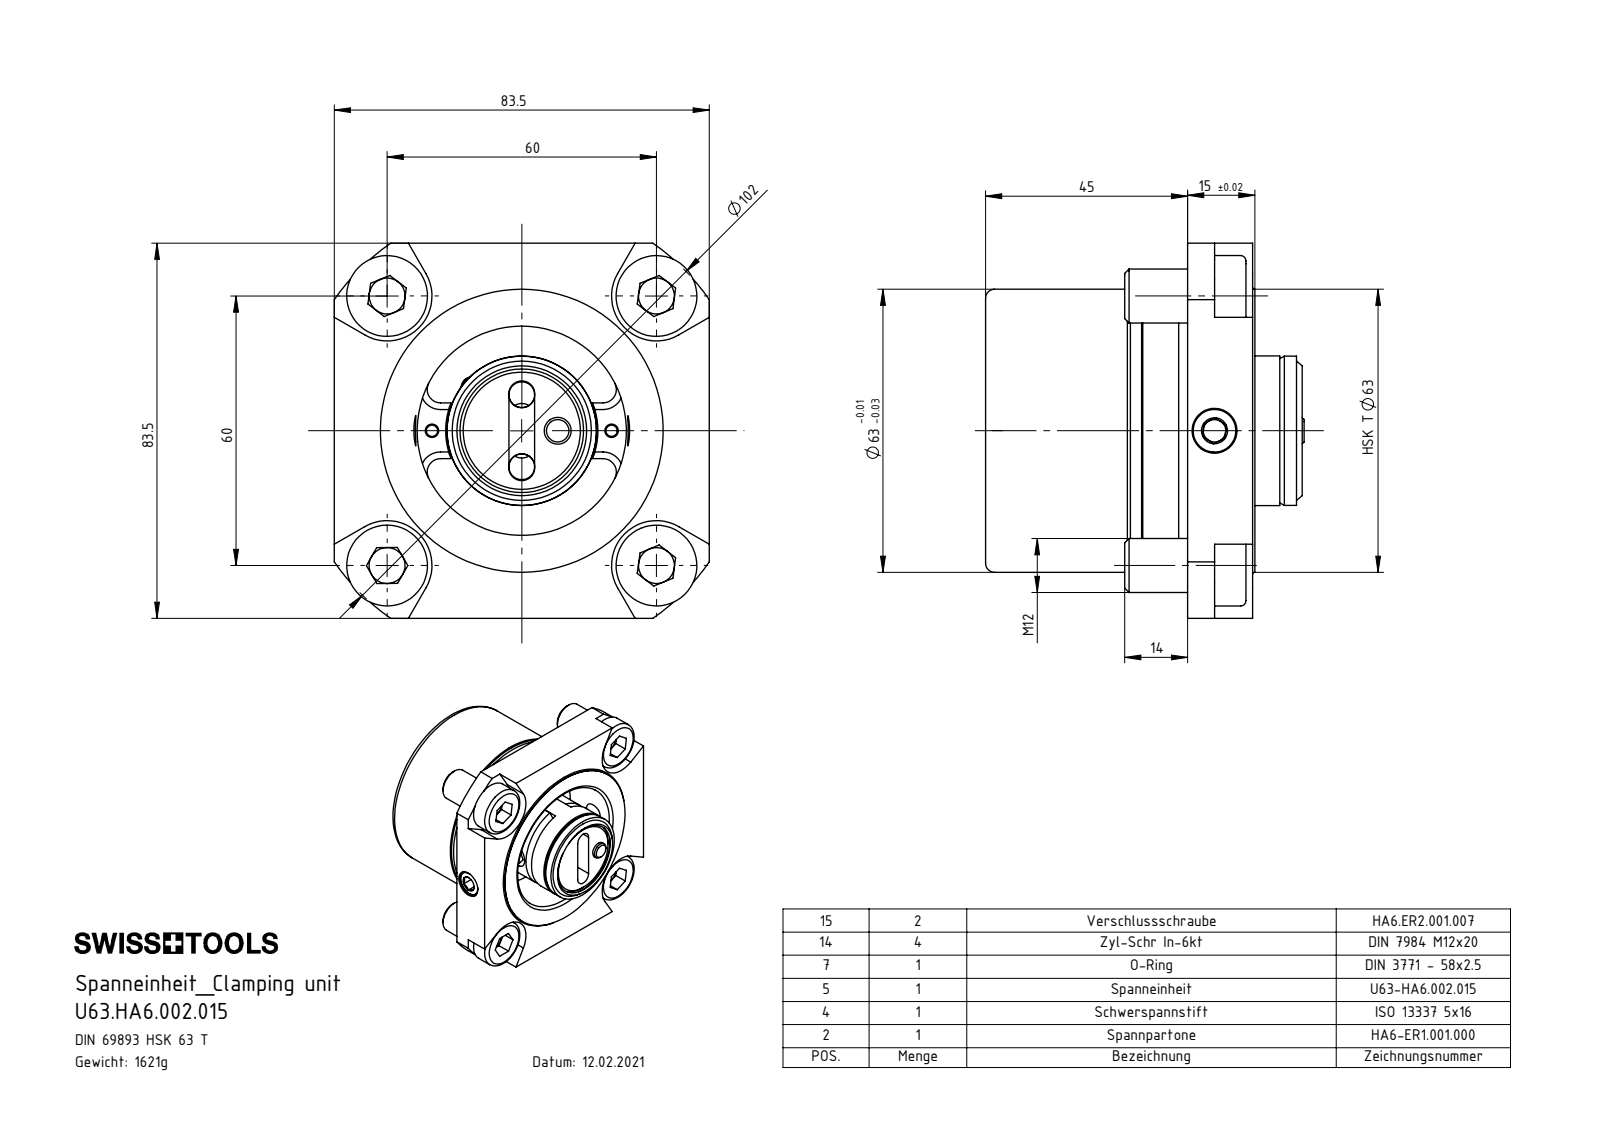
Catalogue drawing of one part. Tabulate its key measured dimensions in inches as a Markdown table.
| quantity | value |
| --- | --- |
| part name | DIN 3771 - 58x2.5; HA6-ER2.001.007; DIN 3771 - 17x2; Backe6 (+8 more) |
| STEP written by | SolidWorks 2022 (AUTOMOTIVE_DESIGN) |
| units | inches |
| bodies | 16 solids, 494 faces (196 planar, 151 cylindrical, 147 other) |
| overall size | 3.287 × 3.287 × 2.793 |
| volume | 12.67 in³ |
| surface area | 100.5 in² |
| round holes (diameter × count) | 0.512 × 4, 0.098 × 2, 0.226 × 2, 0.228 × 2, 0.394 × 2, 0.157 × 1, 0.197 × 1, 0.236 × 1, 0.268 × 1, 0.315 × 1, 0.335 × 1, 0.52 × 1 |
| round bosses / shafts (diameter × count) | 0.709 × 4, 0.472 × 4, 2.48 × 1, 2.461 × 1, 2.313 × 1, 1.311 × 1, 1.309 × 1, 1.299 × 1 |
| partial cylindrical surfaces (radius × count) | 0.118 × 12, 0.114 × 4, 0.394 × 4, 0.039 × 2, 0.113 × 2, 0.159 × 1, 0.433 × 1, 0.61 × 1 |
| main face-to-face distances | 1.772, 2.343, 0.571, 0.335, 3.287, 0.354, 1.486, 1.801, 2.008, 0.236 |
| hole center spacings | 1.465, 1.906, 0.848, 1.245, 1.67, 2.296, 2.362, 0.315 |
